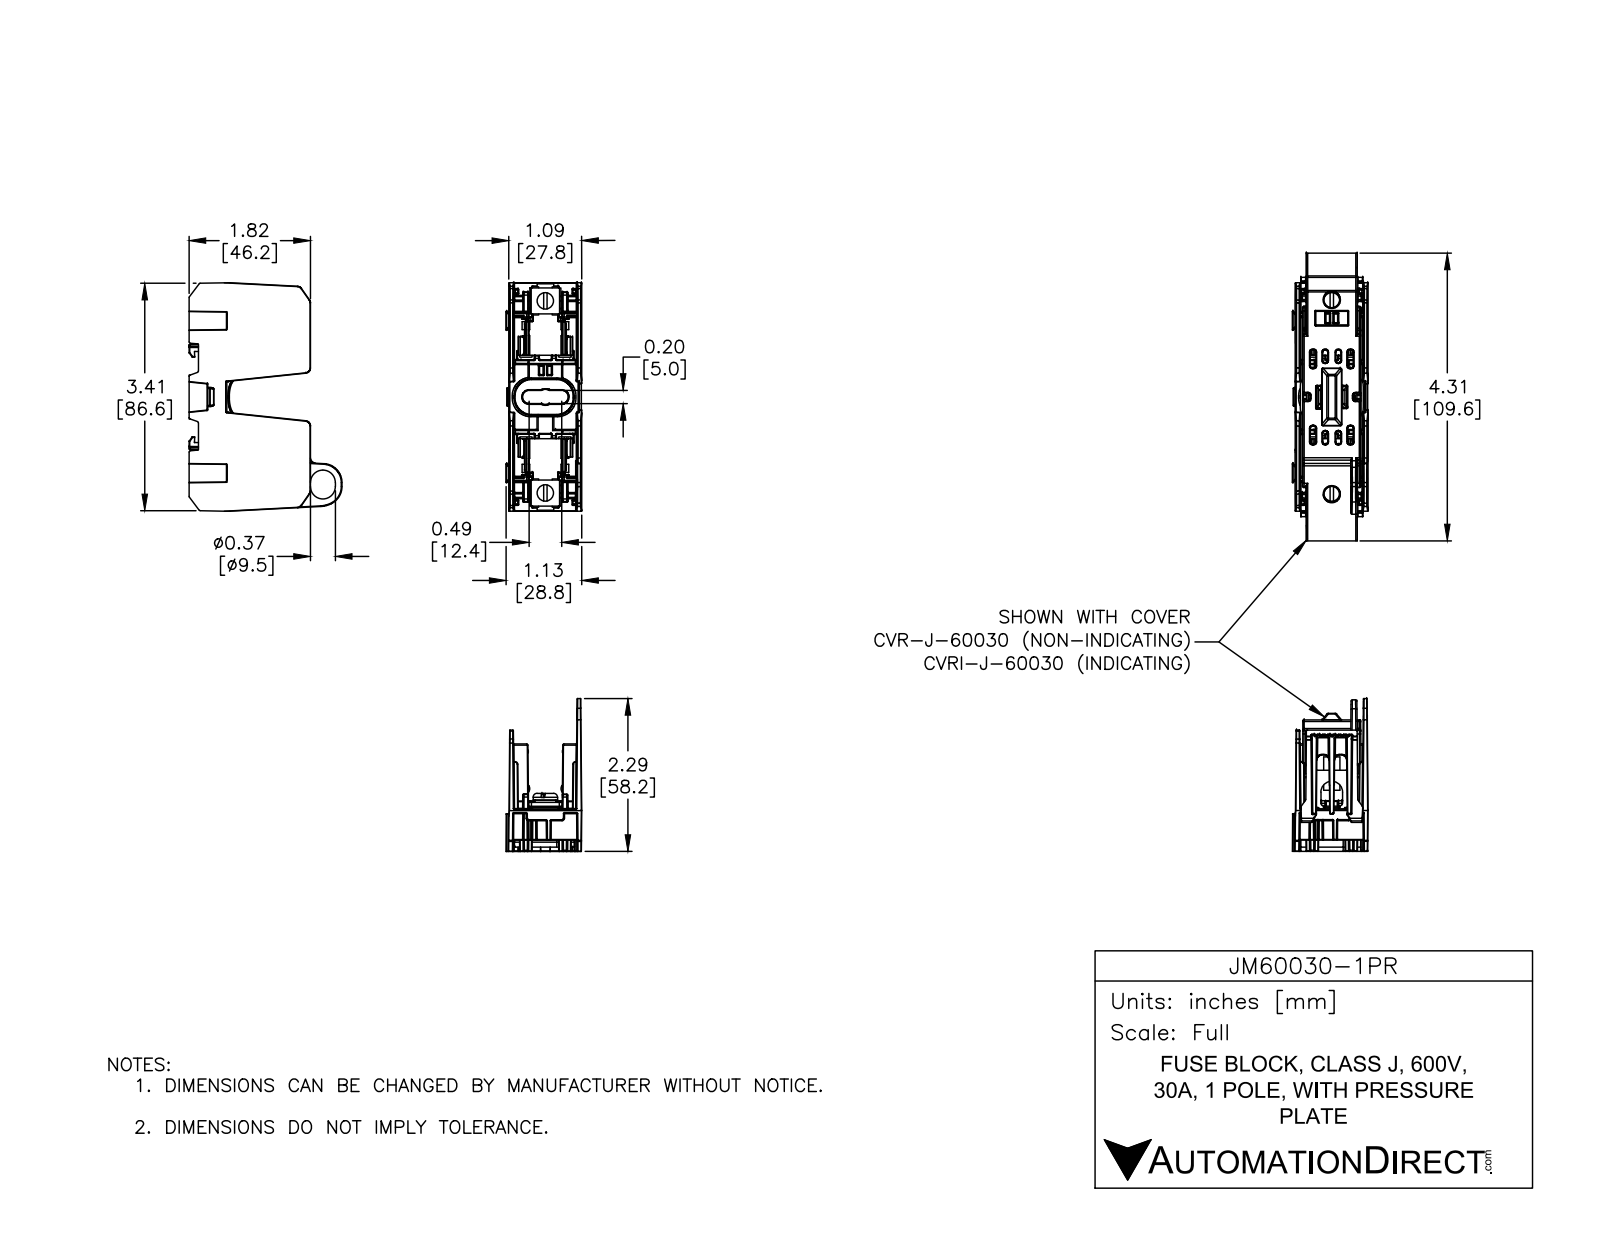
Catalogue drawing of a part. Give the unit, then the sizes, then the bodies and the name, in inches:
Units: inches
Overall size (bounding box): 3.433 × 2.291 × 1.134
Round holes (diameter × count): ⌀0.225 ×2, ⌀0.244 ×2
Round bosses / shafts (diameter × count): ⌀0.244 ×2
Partial cylindrical surfaces — rounded edges, fillets, slot ends (radius × count): R0.01 ×416, R0.006 ×327, R0.02 ×57, R0.039 ×32, R0.004 ×24, R0.079 ×9, R0.02 ×8, R0.049 ×6
Main face-to-face distances: 1.013, 0.024, 1.014, 0.075, 1.089, 0.016, 0.065, 0.07, 0.085, 0.661
Hole centre spacings: 0.595, 2.285, 1.69, 2.88
Volume: 1.976 in³ · Surface area: 51.62 in²
Bodies: 13 solids, 3093 faces (781 planar, 1329 cylindrical, 983 other)
Part name (STEP PRODUCT): JM60030-1PR
STEP written by: SolidWorks 2016 (AUTOMOTIVE_DESIGN)
